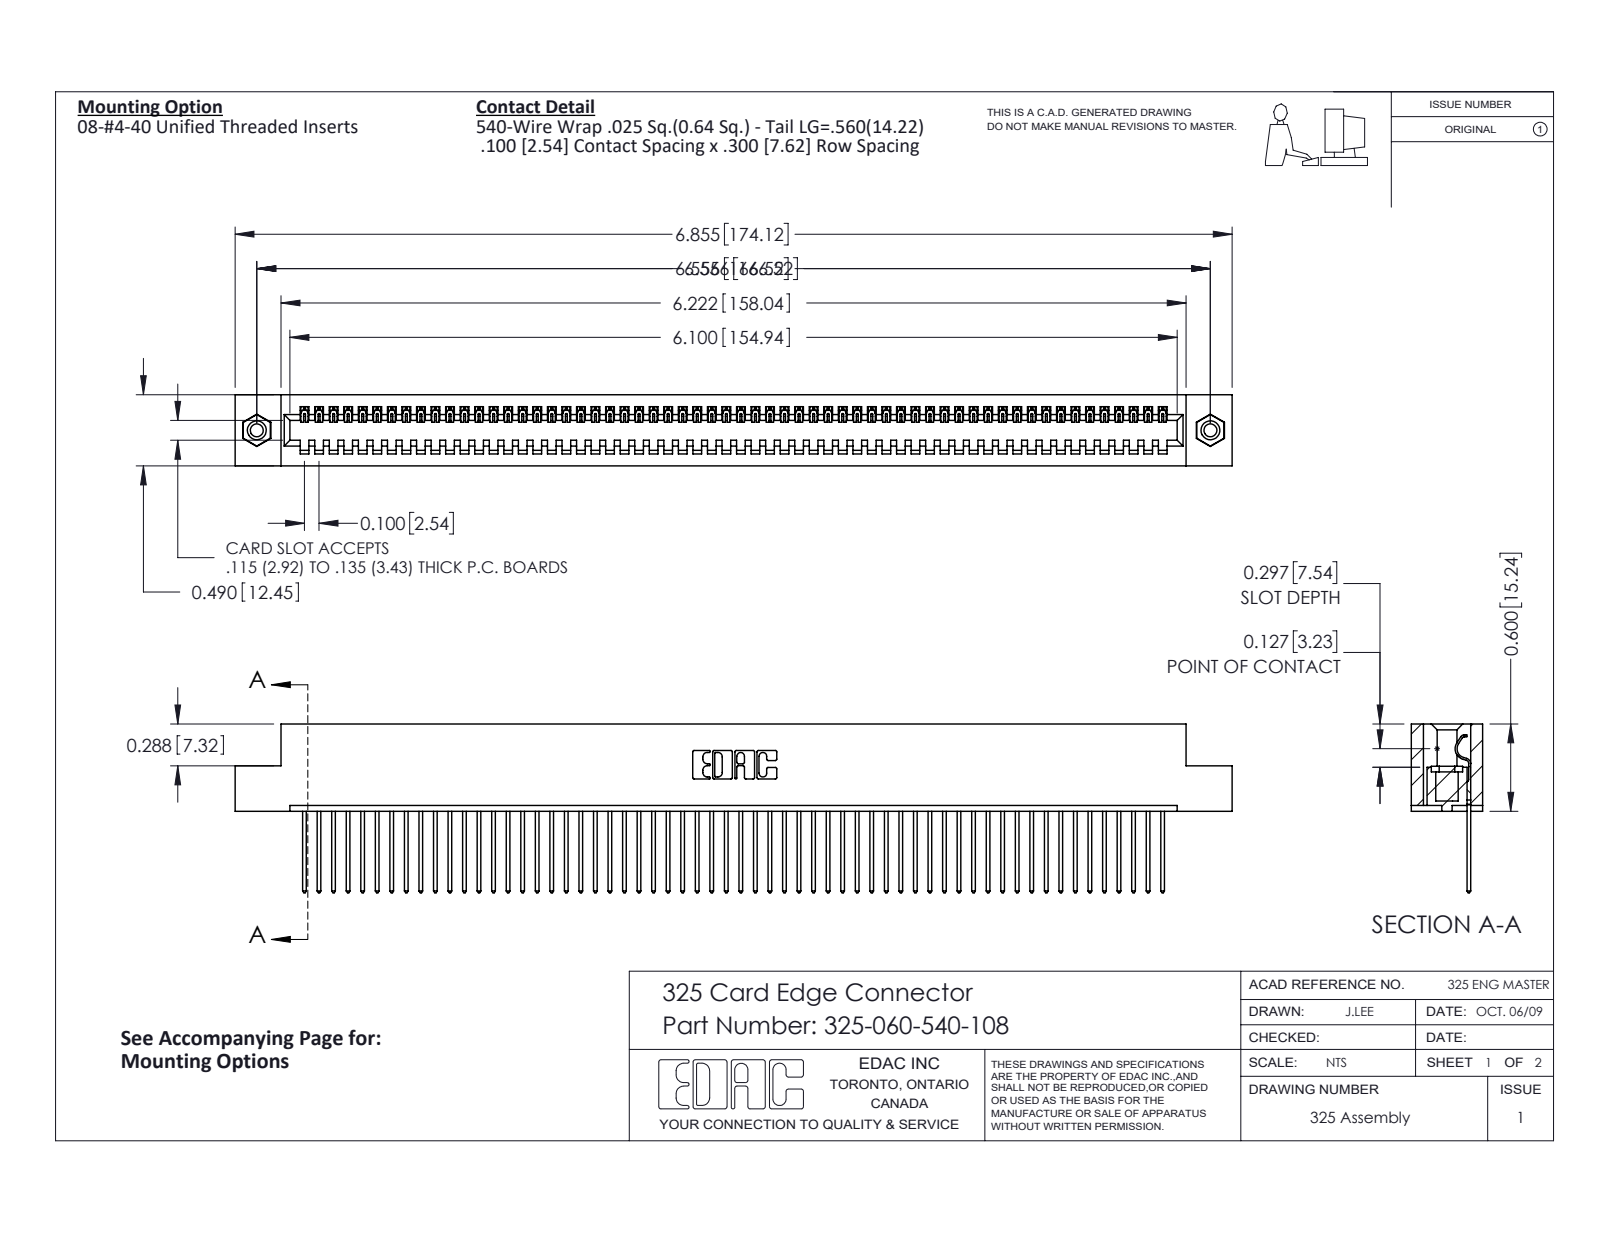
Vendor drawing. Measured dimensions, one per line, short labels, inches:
name: 325-292-001_325-293-140; 325 Part_TI; 345-250-001_345-250-003-102; 325-060-540-108
written by: SolidWorks 2016 (CONFIG_CONTROL_DESIGN)
unit: in
bodies: 63 solids, 3654 faces (2622 planar, 1016 cylindrical, 16 other)
size: 6.855 × 1.16 × 0.49
volume: 1.362 in³; area: 39.23 in²
holes: 2× ⌀0.089, 2× ⌀0.125, 2× ⌀0.16
bosses: 2× ⌀0.155
rounds: 120× R0.006, 120× R0.01, 22× R0.01, 6× R0.007, 6× R0.031, 3× R0.026, 1× R0.014, 1× R0.022
face distances: 0.083, 0.407, 0.49, 0.3, 0.107, 0.383, 0.025, 0.325, 0.56, 0.263
hole spacings: 6.556
